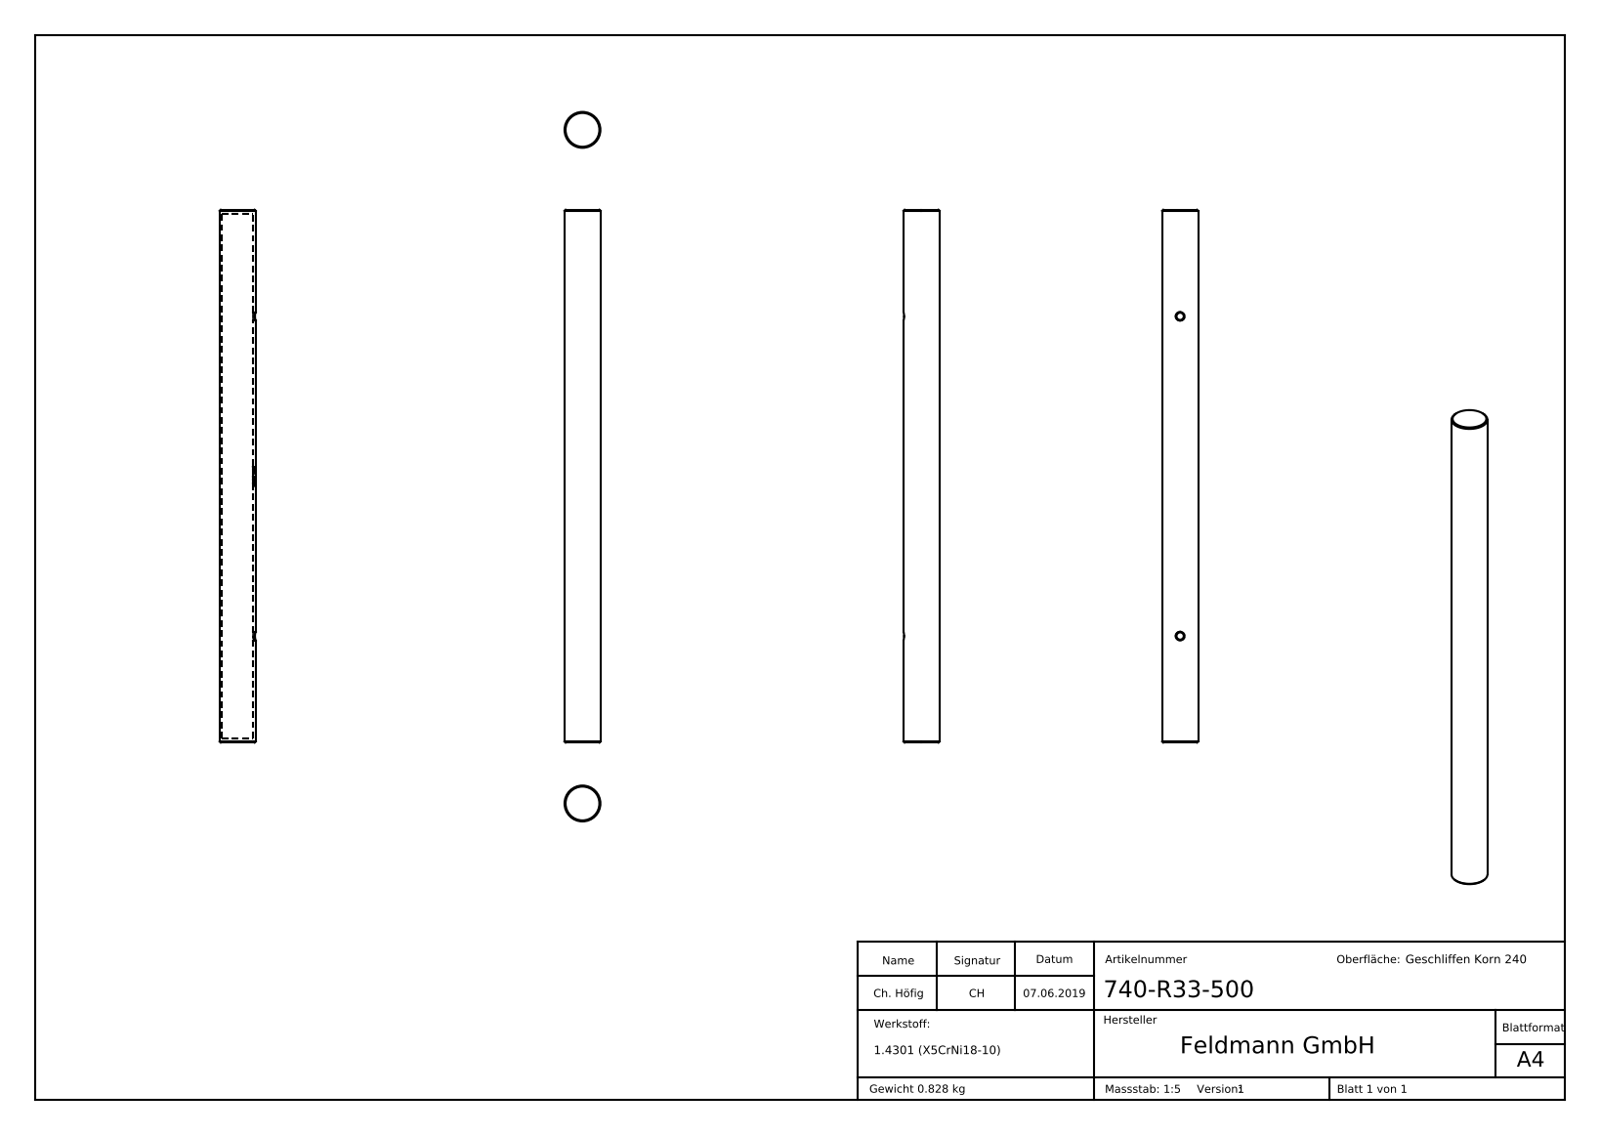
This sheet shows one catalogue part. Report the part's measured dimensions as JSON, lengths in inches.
{"part_name": "740-R33-500", "step_written_by": "SolidWorks 2015 (CONFIG_CONTROL_DESIGN)", "units": "inches", "bodies": {"solids": 1, "faces": 270, "planar": 105, "cylindrical": 35, "other": 130}, "overall_size": [19.685, 1.327, 1.327], "volume_in3": 6.399, "surface_area_in2": 157.8, "round_holes": [[0.268, 2], [1.169, 1]], "round_bosses_or_shafts": [[1.327, 1]], "partial_cylinders_radius": [[0.589, 1]], "face_to_face_distances": [0.157, 19.528, 19.685, 19.37, 0.435, 0.08, 0.084, 0.431, 0.023, 0.515], "hole_center_spacings": [11.811]}
